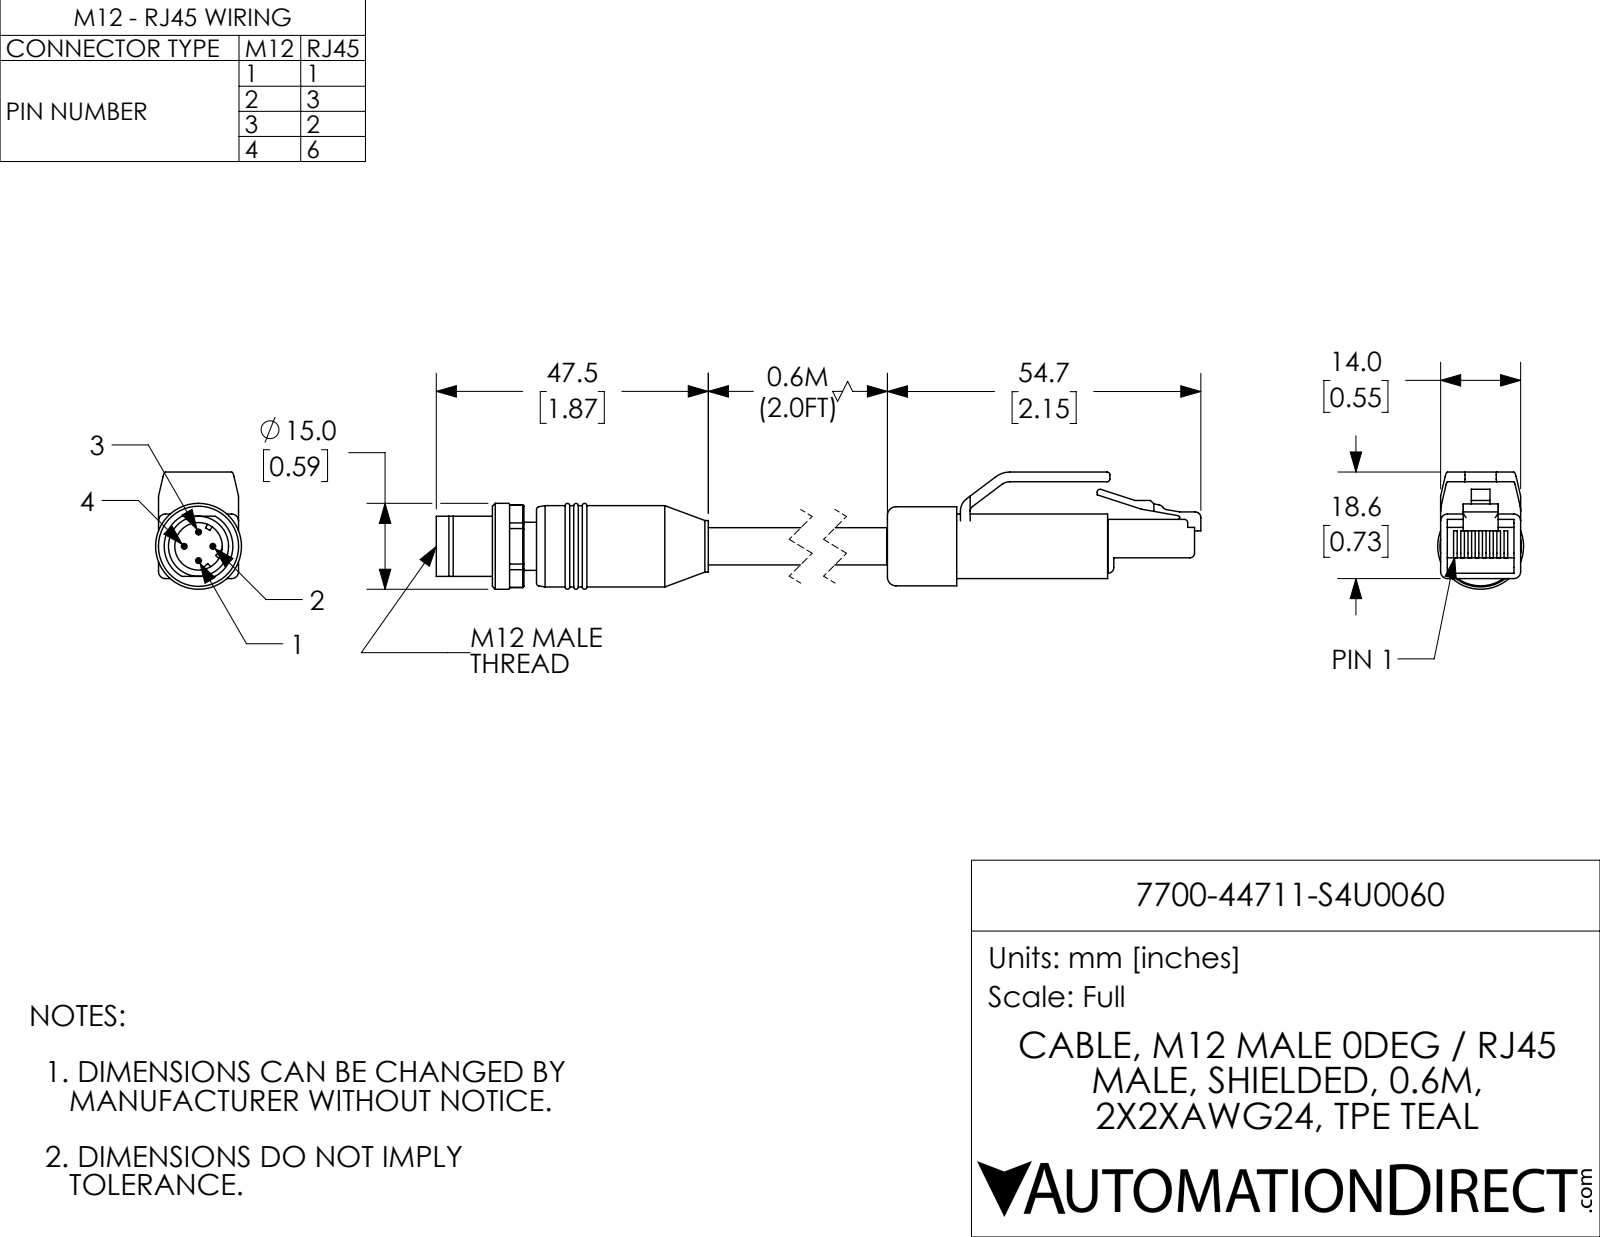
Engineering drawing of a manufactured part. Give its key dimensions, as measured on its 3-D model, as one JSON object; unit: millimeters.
{"part_name": "7700-44711-S4U0060; 7700-44711-S4U0060_RJ45; 7700-44711-S4U0060_MALE", "step_written_by": "SolidWorks 2017 (AUTOMOTIVE_DESIGN)", "units": "millimeters", "bodies": {"solids": 4, "faces": 230, "planar": 121, "cylindrical": 67, "other": 42}, "overall_size": [146.3, 20.5, 15], "volume_mm3": 14700, "surface_area_mm2": 7271, "round_holes": [[8.3, 1]], "round_bosses_or_shafts": [[1, 4], [15, 1], [14.2, 1], [13.8, 1], [10.5, 1], [9, 1], [8.4, 1], [6.5, 1]], "partial_cylinders_radius": [[1.2, 6], [0.5, 5], [1, 5], [0.3, 2], [0.6, 1], [0.8, 1], [2.3, 1], [2.7, 1]], "face_to_face_distances": [11.3, 14, 1.7, 3.6, 7.6, 10.3, 6.7, 0.9, 16.9, 18.6]}
